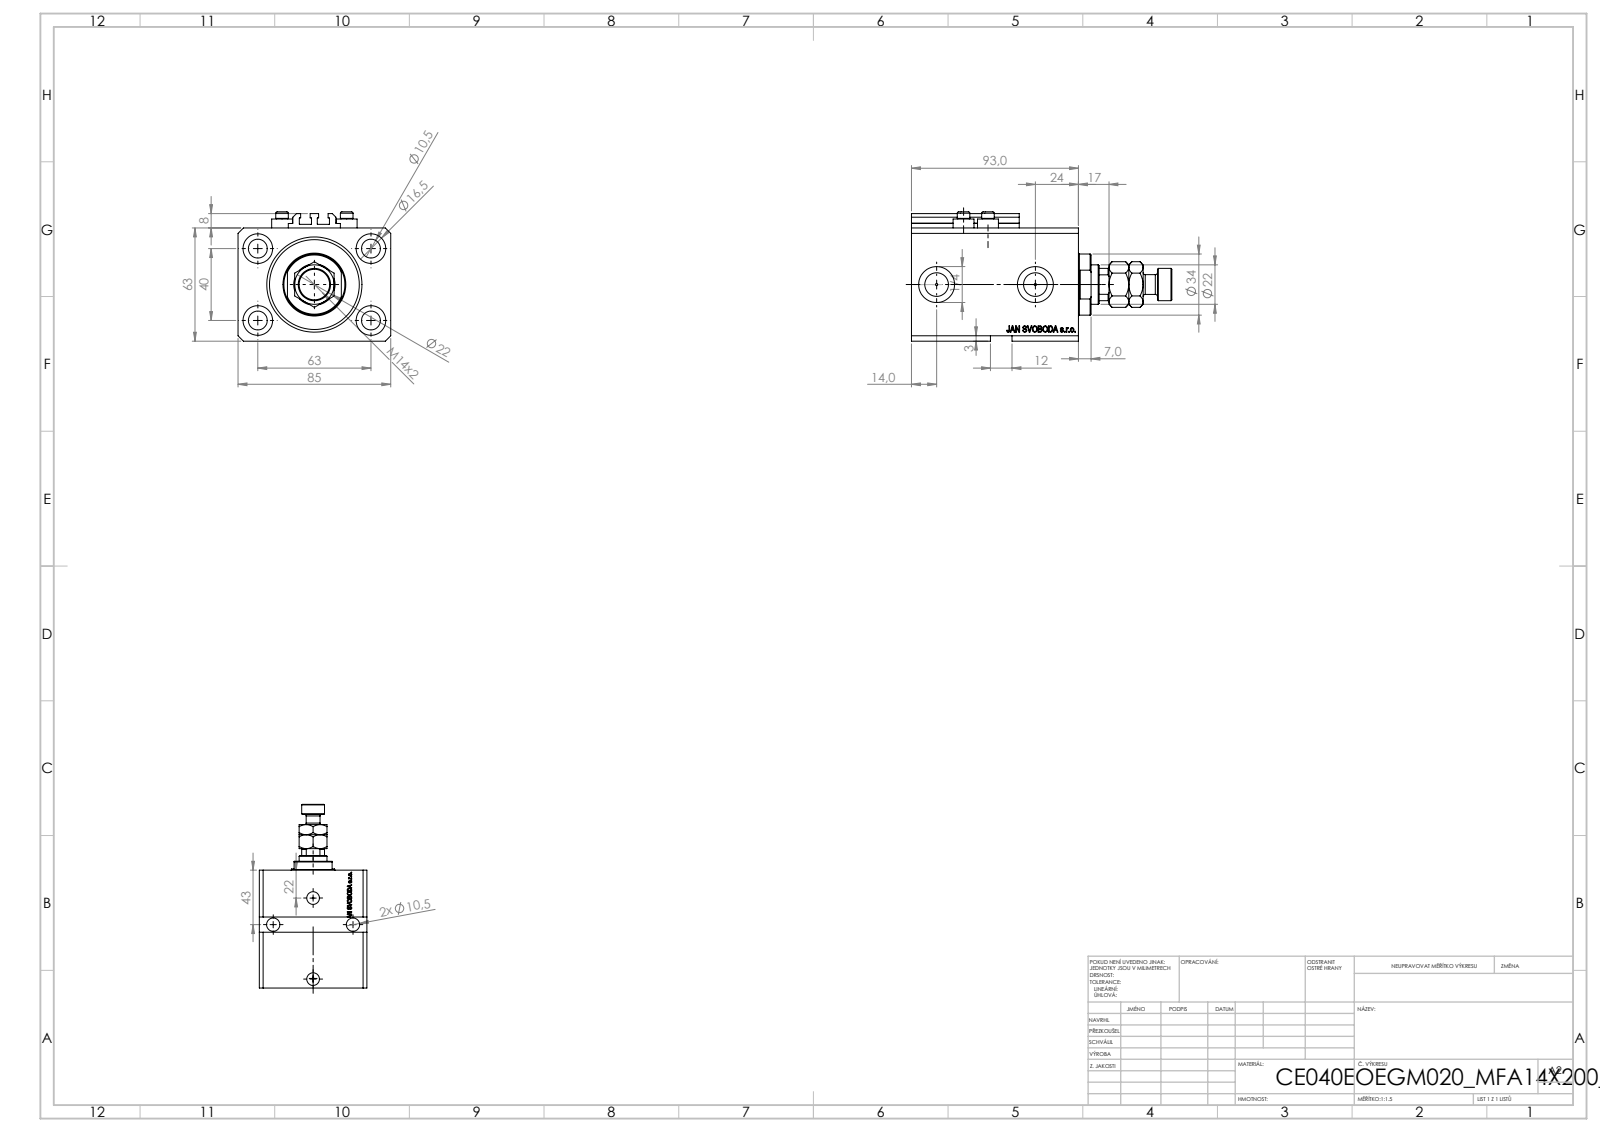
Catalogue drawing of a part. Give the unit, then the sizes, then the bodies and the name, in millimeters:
Units: millimetres
Overall size (bounding box): 145 × 85 × 72
Round holes (diameter × count): ⌀10.5 ×6, ⌀1.25 ×4, ⌀4 ×4, ⌀16.5 ×4, ⌀10 ×2, ⌀13.16 ×2, ⌀20 ×2, ⌀12.5 ×1, ⌀22 ×1, ⌀40 ×1, ⌀53 ×1
Round bosses / shafts (diameter × count): ⌀11.6 ×4, ⌀7 ×4, ⌀34 ×1, ⌀18 ×1, ⌀11 ×1
Partial cylindrical surfaces — rounded edges, fillets, slot ends (radius × count): R0.2 ×10, R10.5 ×1
Main face-to-face distances: 63, 85, 93, 17, 76, 11.4, 64.6, 81.6, 3, 65
Hole centre spacings: 37.31, 63, 13.6, 15.4, 24.96, 28.02, 28.43, 33.62
Volume: 447 941 mm³ · Surface area: 99 017 mm²
Bodies: 9 solids, 1139 faces (551 planar, 130 cylindrical, 458 other)
Part name (STEP PRODUCT): V250CE_E_Body; V250CE_VC_E; MFA; V250CE_C_VCP (+1 more)
STEP written by: SolidWorks 2019 (CONFIG_CONTROL_DESIGN)
